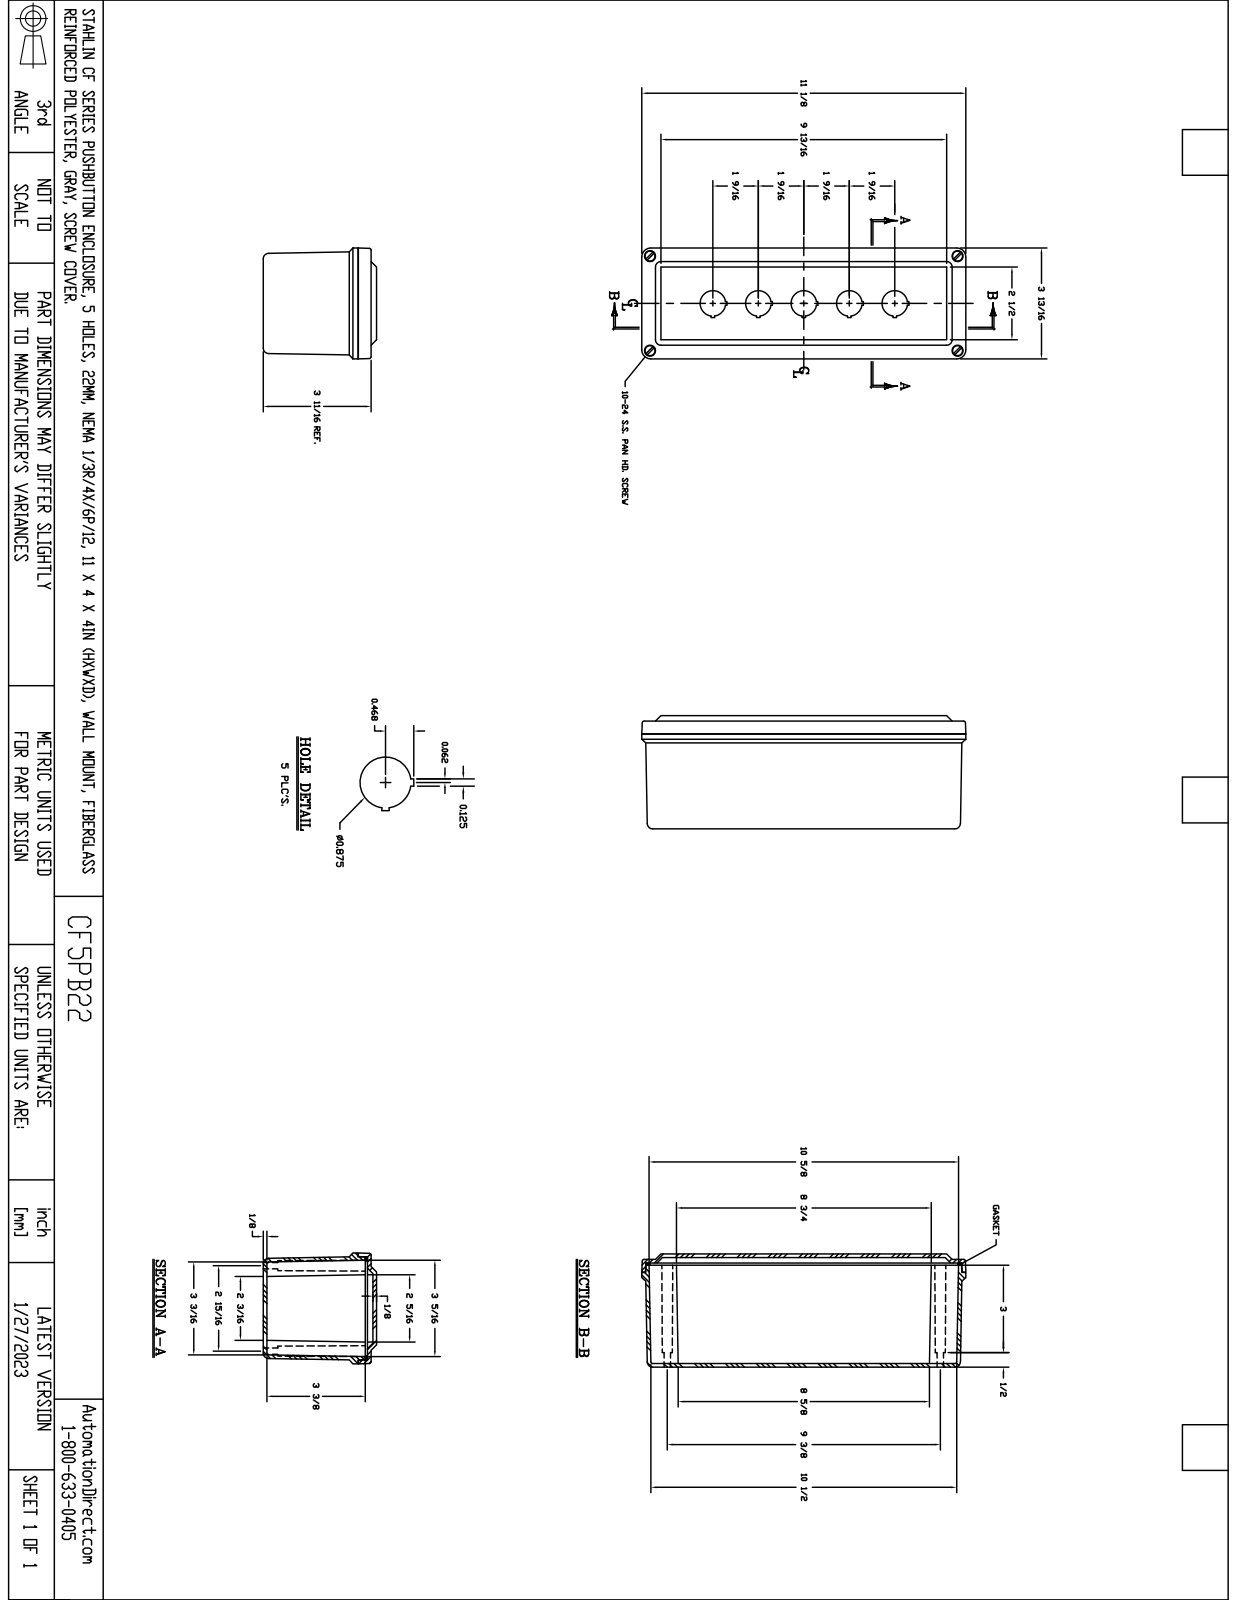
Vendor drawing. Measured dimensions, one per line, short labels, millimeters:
name: CO5PB22
written by: SolidWorks 2018 (AUTOMOTIVE_DESIGN)
unit: mm
bodies: 11 solids, 415 faces (197 planar, 122 cylindrical, 96 other)
size: 350.1 × 92.1 × 79.2
volume: 446 400 mm³; area: 269 800 mm²
holes: 8× ⌀5.6, 4× ⌀4, 4× ⌀4.8, 4× ⌀9.5, 3× ⌀22.2, 1× ⌀22.2
bosses: 4× ⌀9.4, 4× ⌀6.9, 4× ⌀4.5
rounds: 20× R0.8, 16× R0.3, 8× R1.2, 4× R1.6, 4× R4.5, 4× R4.8, 4× R5.6, 4× R8
face distances: 3.2, 3.1, 76.1, 79.2, 72.9, 71.3, 4.7, 8, 3.2, 1.6
hole spacings: 10.4, 73.7, 122.6, 133, 161, 171.4, 199.9, 210.3
